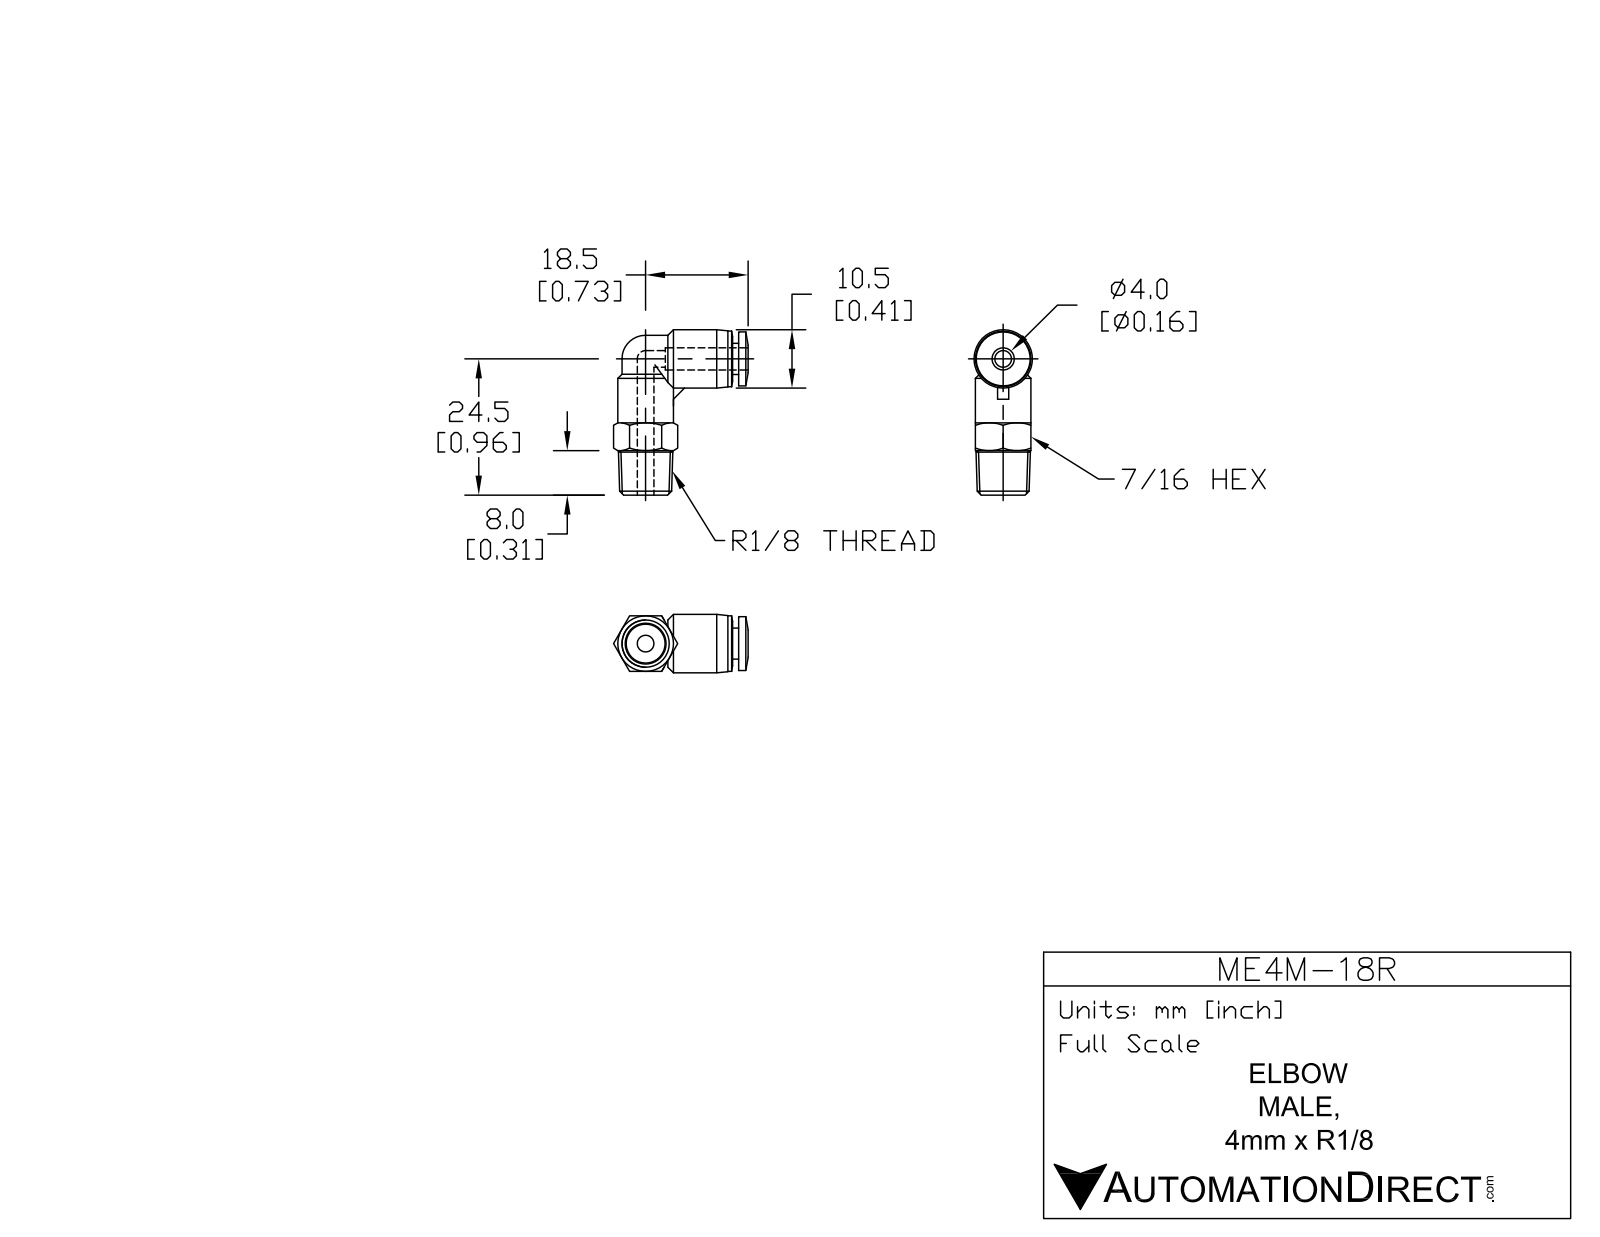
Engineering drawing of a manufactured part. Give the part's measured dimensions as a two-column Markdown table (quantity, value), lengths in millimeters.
| quantity | value |
| --- | --- |
| part name | ME4M-18R |
| STEP written by | SolidWorks 2015 (AUTOMOTIVE_DESIGN) |
| units | millimeters |
| bodies | 1 solid, 68 faces (16 planar, 19 cylindrical, 33 other) |
| overall size | 29.7 × 24.2 × 10.5 |
| volume | 2 740 mm³ |
| surface area | 1 988 mm² |
| round holes (diameter × count) | 3 × 2, 4.3 × 1 |
| round bosses / shafts (diameter × count) | 10 × 2, 10.5 × 1, 9.7 × 1, 5.6 × 1 |
| partial cylindrical surfaces (radius × count) | 4.2 × 2 |
| main face-to-face distances | 10, 1.1, 12, 13.1, 4, 6, 8, 2, 11.2, 0.8 |
